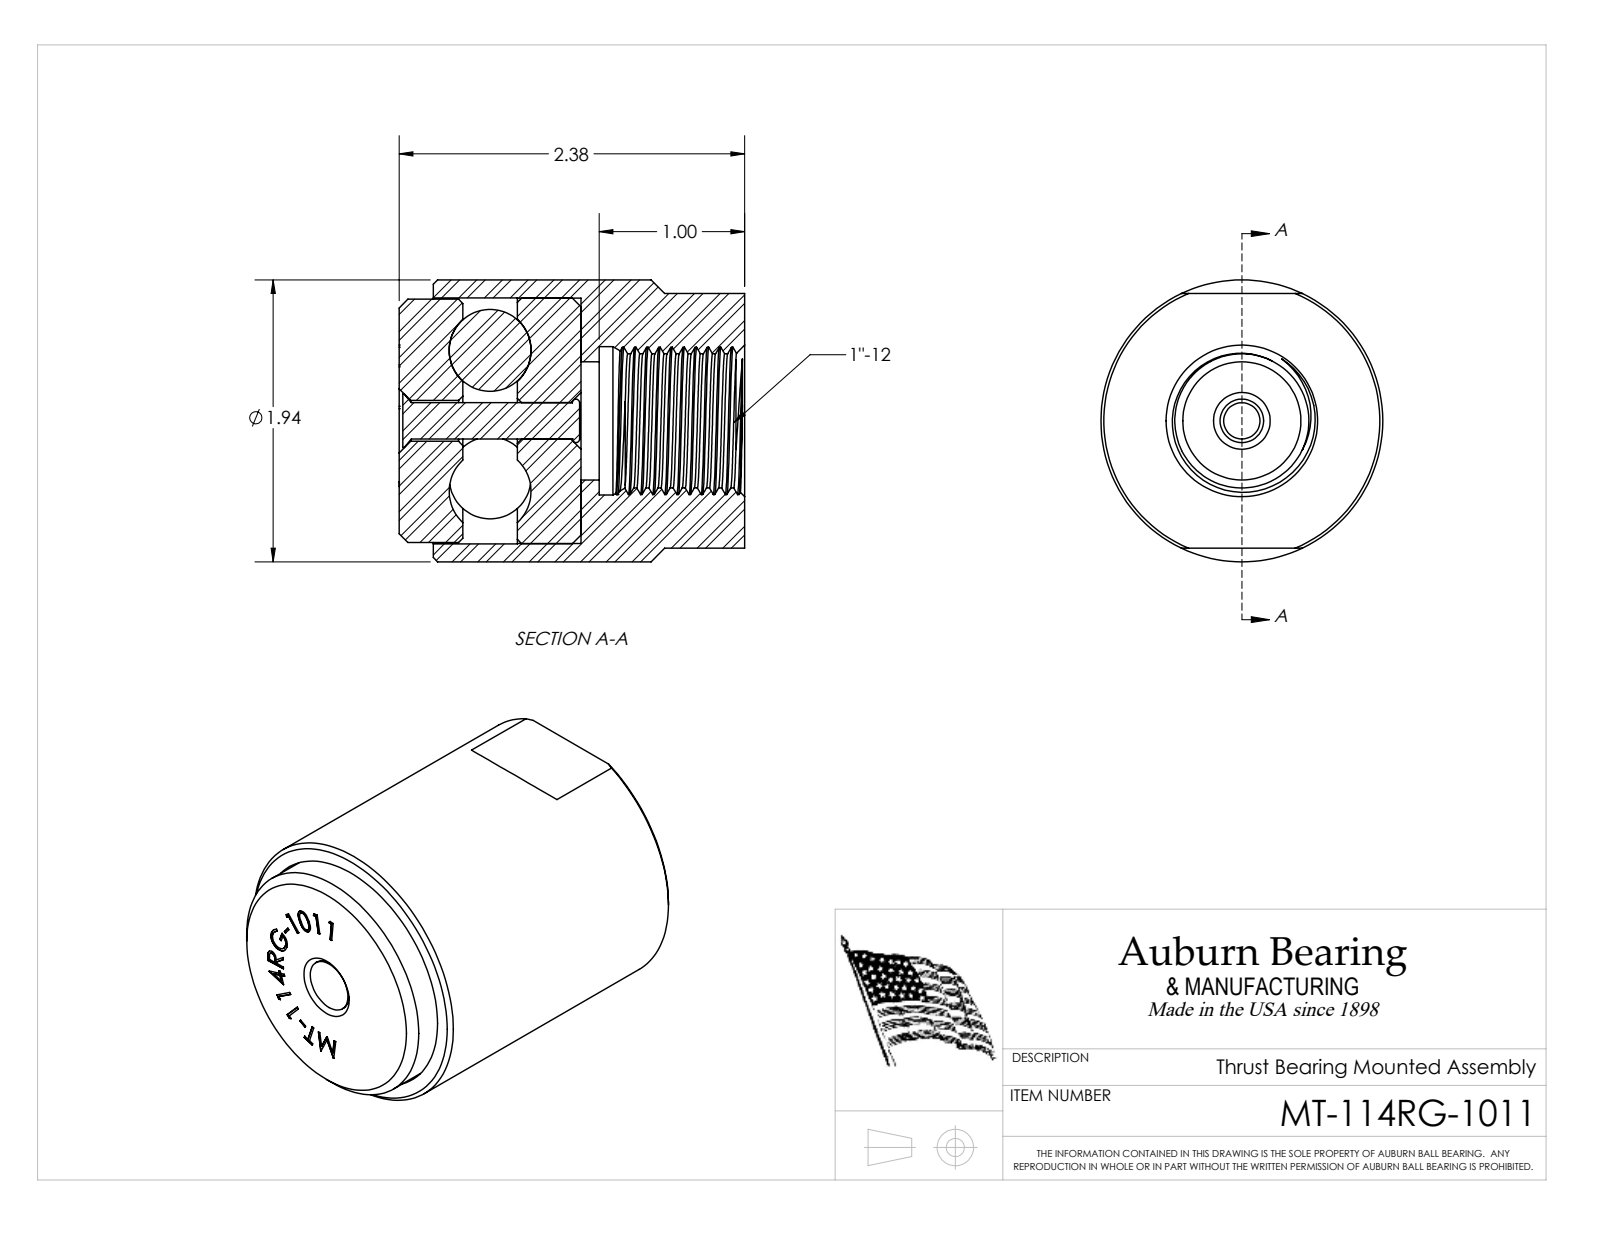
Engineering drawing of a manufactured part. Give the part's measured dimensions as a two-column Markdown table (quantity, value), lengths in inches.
| quantity | value |
| --- | --- |
| part name | MT-114RG-1011 |
| STEP written by | SolidWorks 2020 (CONFIG_CONTROL_DESIGN) |
| units | inches |
| bodies | 9 solids, 235 faces (121 planar, 42 cylindrical, 72 other) |
| overall size | 2.375 × 1.938 × 1.938 |
| volume | 5.386 in³ |
| surface area | 47.82 in² |
| round holes (diameter × count) | 0.25 × 1, 0.281 × 1, 0.812 × 1, 0.922 × 1, 1.02 × 1, 1.687 × 1, 1.69 × 1 |
| round bosses / shafts (diameter × count) | 1.937 × 1, 1.687 × 1, 1.672 × 1, 0.366 × 1 |
| main face-to-face distances | 1.125, 1.25, 2.375, 0.438, 0.812, 1.563, 0.374, 1.937, 0.234, 0.204 |
